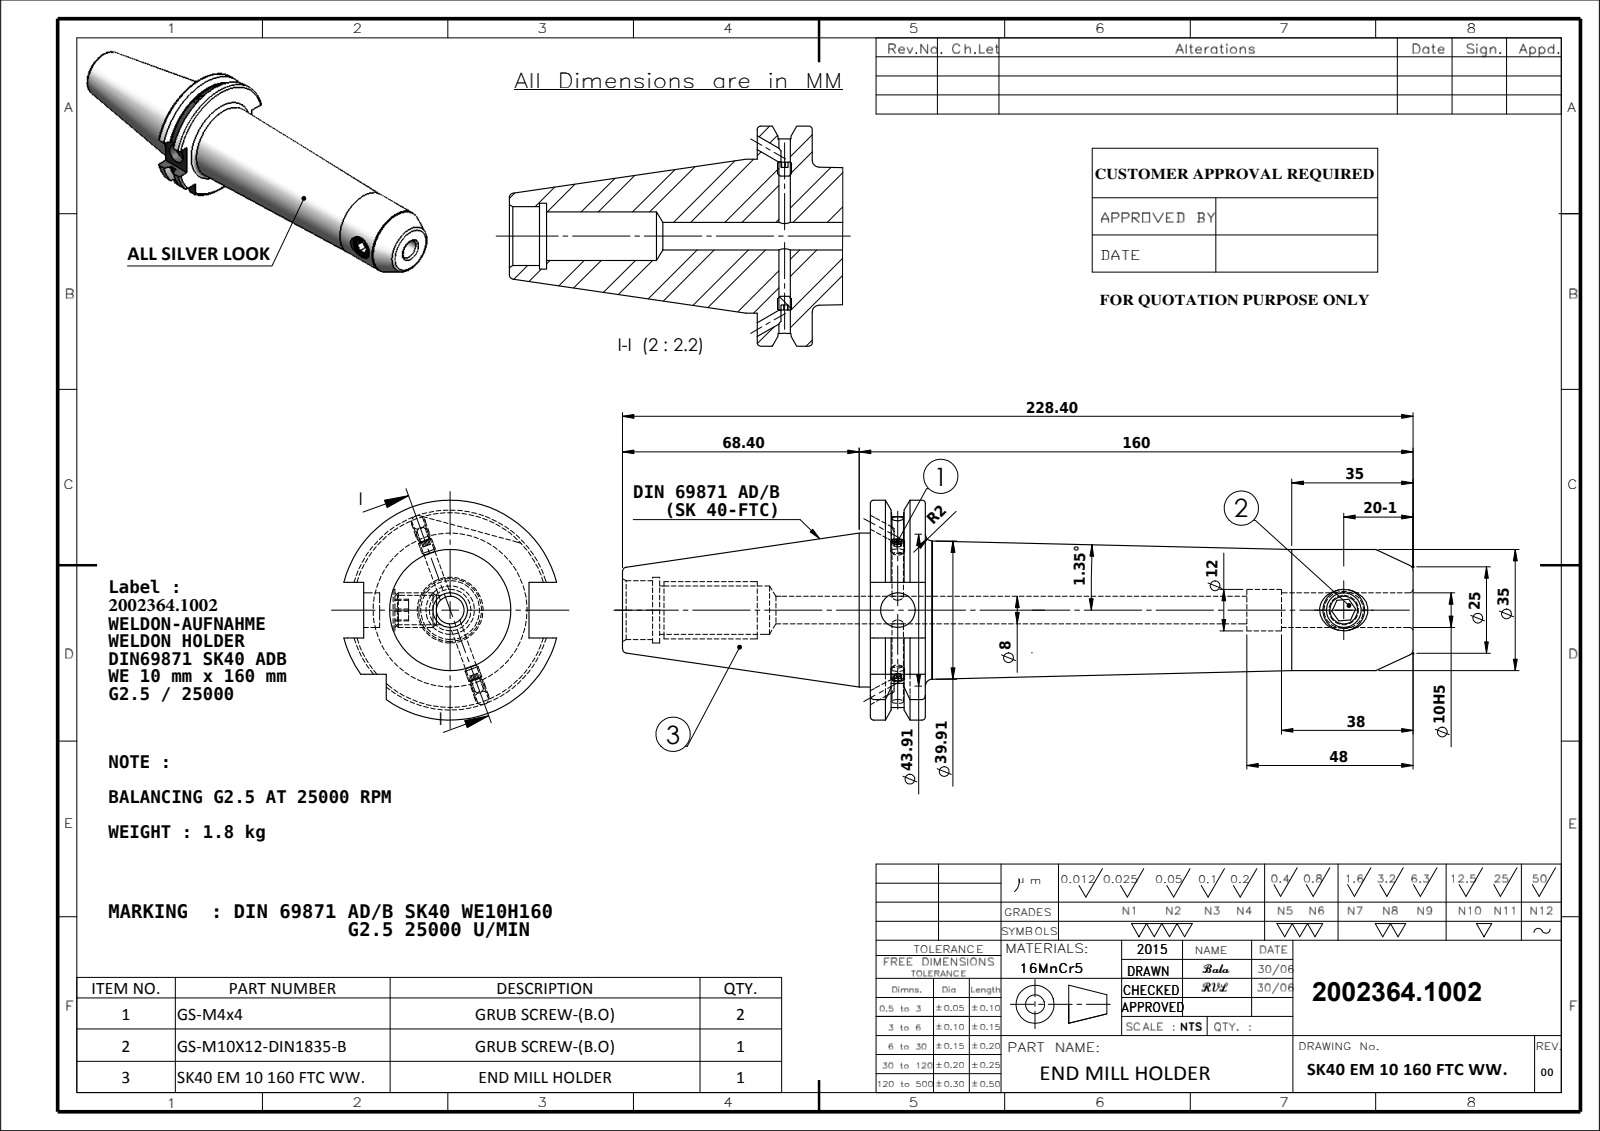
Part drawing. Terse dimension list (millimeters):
name: SK40 EM 10 160 FTC WW.; M10X12; 91406-WE710160; Copy of M4X4_DIN 913 - M4 x 4-N
written by: SolidWorks 2009 (CONFIG_CONTROL_DESIGN)
unit: mm
bodies: 4 solids, 160 faces (58 planar, 44 cylindrical, 58 other)
size: 228.4 × 63.55 × 61.48
volume: 242 103 mm³; area: 40 990 mm²
holes: 2× ⌀10, 2× ⌀12, 1× ⌀3.3, 1× ⌀8, 1× ⌀8.5, 1× ⌀14, 1× ⌀17, 1× ⌀19
bosses: 2× ⌀4, 1× ⌀44.45, 1× ⌀35, 1× ⌀10
rounds: 1× R28.12, 1× R31.77
face distances: 15.9, 156.8, 140.9, 16.1, 47.8, 71.6, 87.5, 228.4, 10.7, 60.9
hole spacings: 128.85
